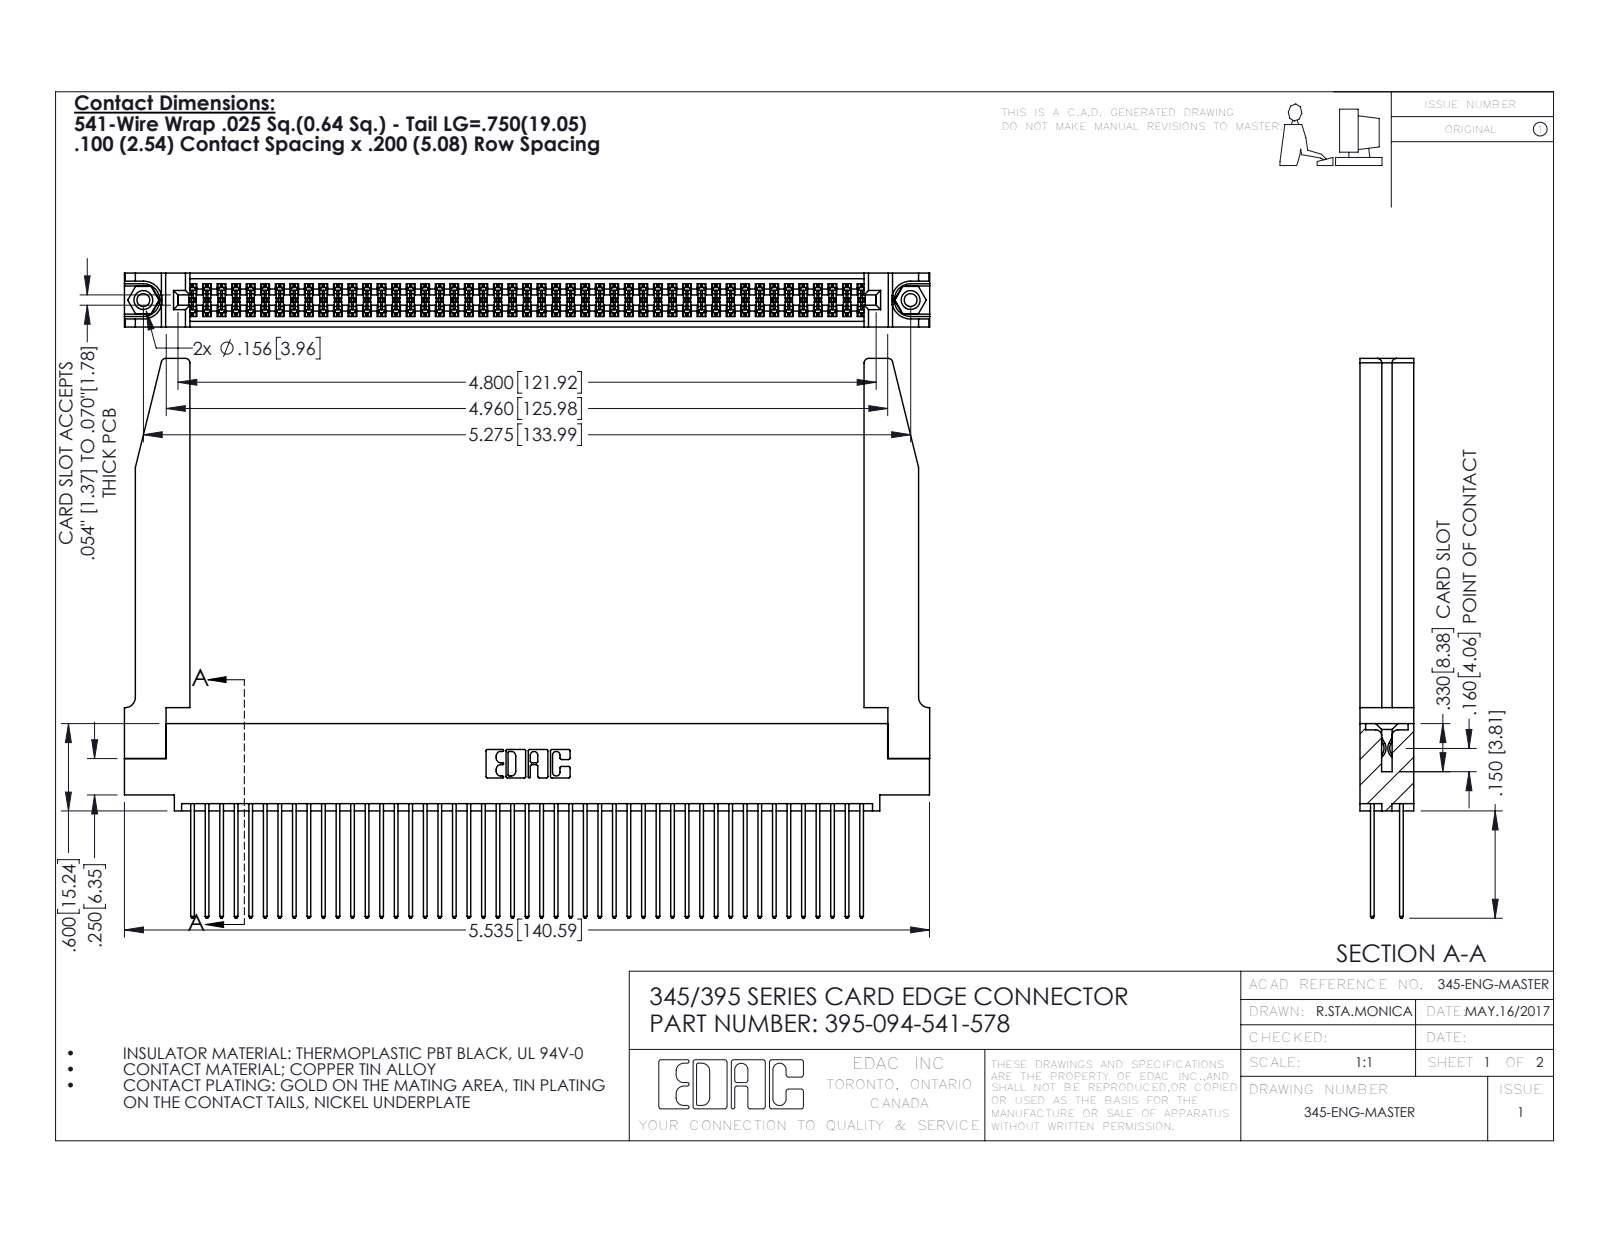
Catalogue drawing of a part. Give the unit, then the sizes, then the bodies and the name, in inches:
Units: inches
Overall size (bounding box): 5.536 × 3.847 × 0.37
Round holes (diameter × count): ⌀0.089 ×2, ⌀0.125 ×2, ⌀0.156 ×2, ⌀0.064 ×1
Round bosses / shafts (diameter × count): ⌀0.155 ×2
Partial cylindrical surfaces — rounded edges, fillets, slot ends (radius × count): R0.006 ×141, R0.01 ×94, R0.01 ×22, R0.03 ×8, R0.007 ×6, R0.031 ×6, R0.026 ×3, R0.014 ×2
Main face-to-face distances: 0.072, 0.298, 0.37, 0.098, 0.272, 0.025, 0.2, 0.225, 0.175, 0.148
Hole centre spacings: 0.27, 5.039, 5.275
Volume: 1.339 in³ · Surface area: 47.29 in²
Bodies: 99 solids, 5064 faces (3328 planar, 1684 cylindrical, 52 other)
Part name (STEP PRODUCT): 345-292-001_345-293-141; 345-220-078_345-220-078; 395-094-541-578; 345-250-001_345-250-001-102 (+1 more)
STEP written by: SolidWorks 2016 (CONFIG_CONTROL_DESIGN)
